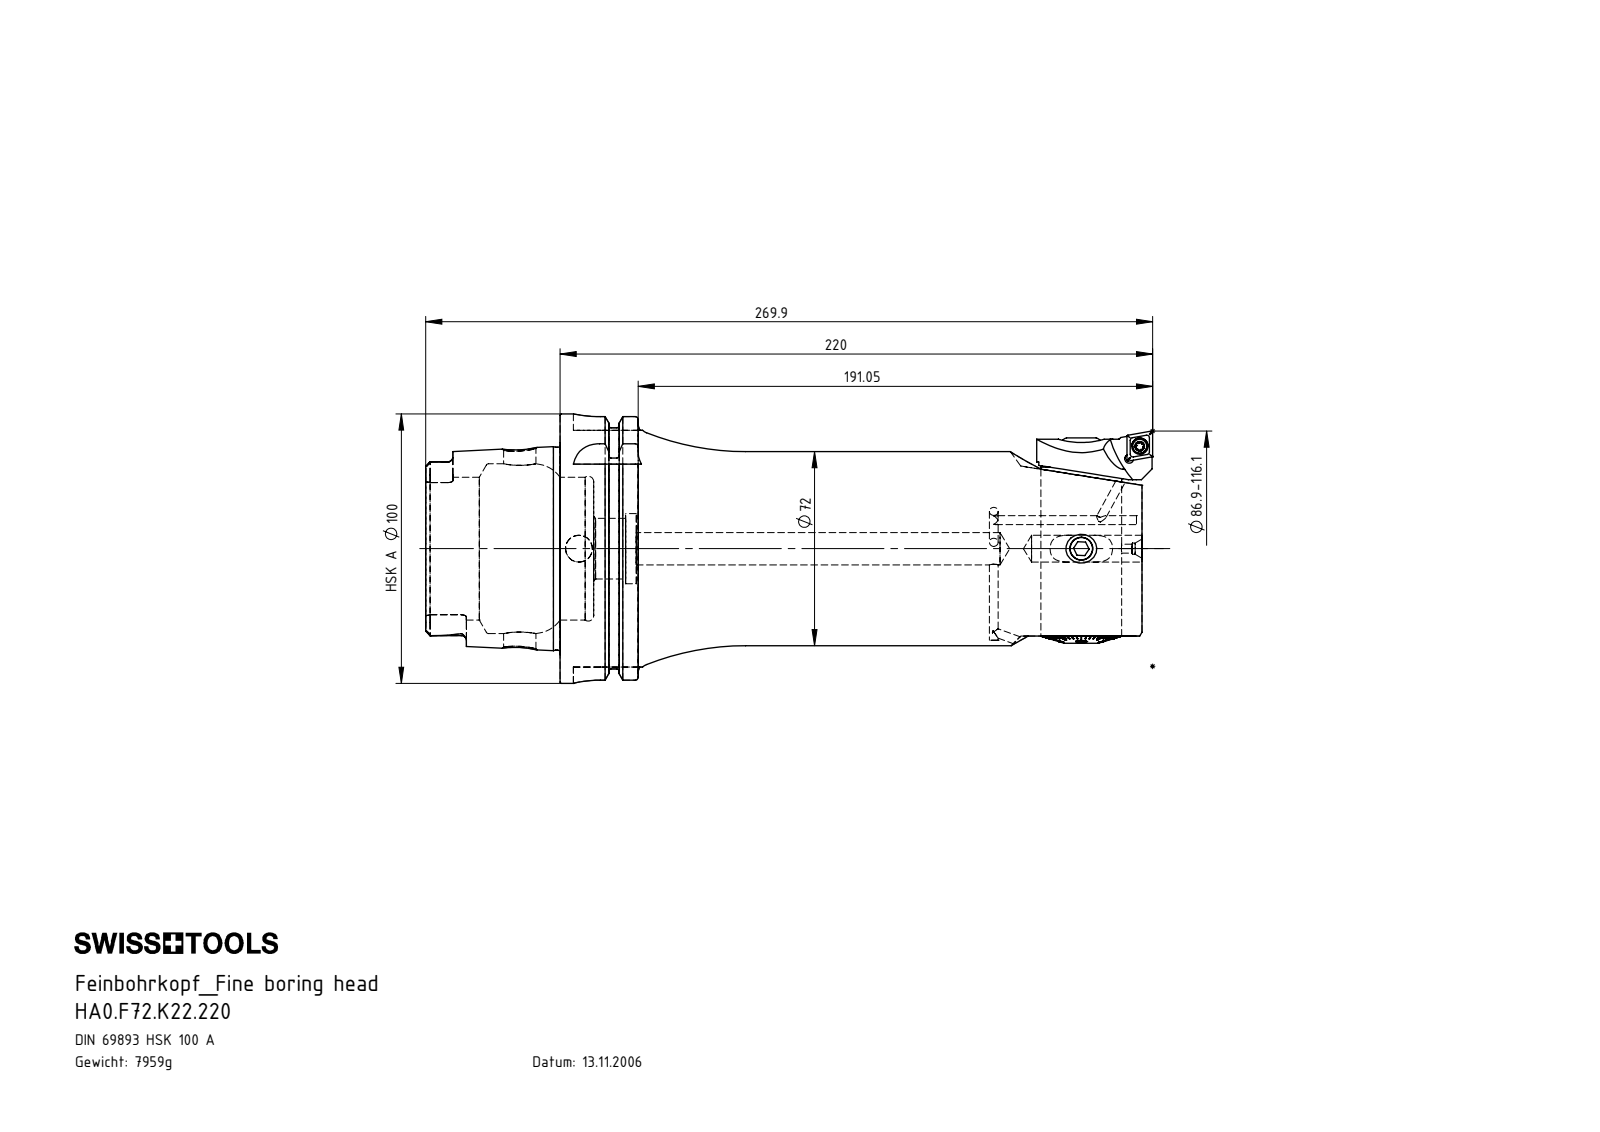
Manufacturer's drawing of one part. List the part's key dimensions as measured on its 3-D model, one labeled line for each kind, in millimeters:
Part name (STEP PRODUCT): A55-BG3.011.033_A_gekürzt; CCMT09T304; F72-BG1.014.056; Klebstoff D10 (+8 more)
STEP written by: SolidWorks 2022 (AUTOMOTIVE_DESIGN)
Units: millimetres
Bodies: 16 solids, 954 faces (366 planar, 207 cylindrical, 381 other)
Overall size (bounding box): 269.9 × 100 × 100
Volume: 995 739 mm³ · Surface area: 125 487 mm²
Round holes (diameter × count): ⌀3.3 ×9, ⌀12 ×3, ⌀8.5 ×2, ⌀10 ×2, ⌀4.2 ×1, ⌀4.4 ×1, ⌀5 ×1, ⌀6.1 ×1, ⌀8 ×1, ⌀11 ×1, ⌀11.75 ×1, ⌀12.4 ×1
Round bosses / shafts (diameter × count): ⌀10 ×2, ⌀5.25 ×2, ⌀4 ×2, ⌀100 ×1, ⌀91.95 ×1, ⌀75.26 ×1, ⌀72 ×1, ⌀29.98 ×1
Partial cylindrical surfaces — rounded edges, fillets, slot ends (radius × count): R0.34 ×12, R0.59 ×12, R1.9 ×6, R10 ×6, R0.5 ×4, R4.88 ×4, R3.2 ×3, R1 ×1
Main face-to-face distances: 216, 12.45, 203.55, 28.95, 16.5, 187.05, 49.9, 62.35, 78.85, 265.9
Hole centre spacings: 5.72, 5.86, 14.05, 14.5, 26, 32.5, 176, 186.5
